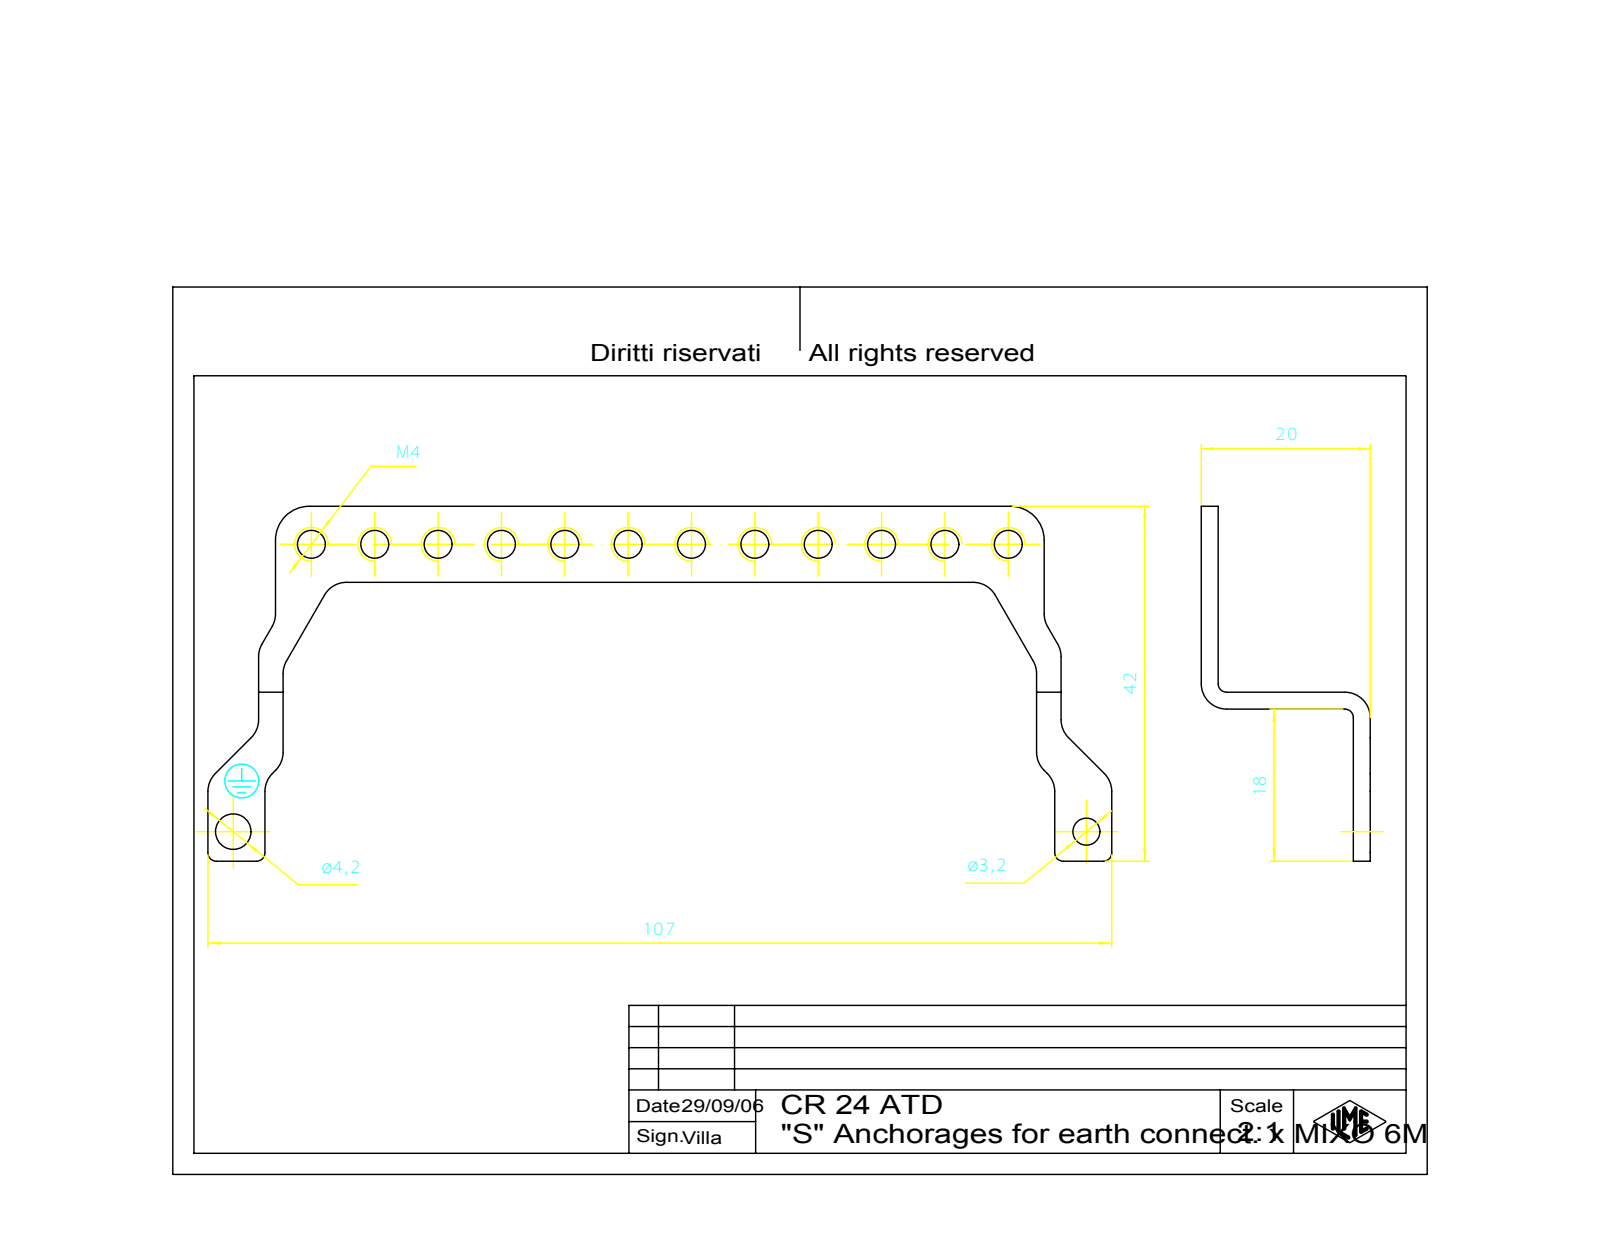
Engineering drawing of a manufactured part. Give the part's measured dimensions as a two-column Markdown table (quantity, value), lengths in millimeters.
| quantity | value |
| --- | --- |
| part name | CR_24_ATD |
| STEP written by | CoCreate Modeling 16.00A 16-Aug-2008 (C) Parametric Technology GmbH (AUTOMOTIVE_DESIGN) |
| units | millimeters |
| bodies | 1 solid, 199 faces (145 planar, 50 cylindrical, 4 other) |
| overall size | 108 × 42.5 × 23.76 |
| volume | 2 353 mm³ |
| surface area | 3 715 mm² |
| round holes (diameter × count) | 4 × 12, 3.2 × 1, 4.2 × 1, 4.3 × 1 |
| round bosses / shafts (diameter × count) | 8 × 1, 6.8 × 1, 6 × 1, 4 × 1, 2.6 × 1 |
| partial cylindrical surfaces (radius × count) | 3 × 4, 4 × 2 |
| main face-to-face distances | 2, 18, 20, 16, 9, 2.9, 92.1, 15, 24, 13 |
| hole center spacings | 7.5, 15, 22.5, 30, 37.5, 45, 52.5, 60 |
